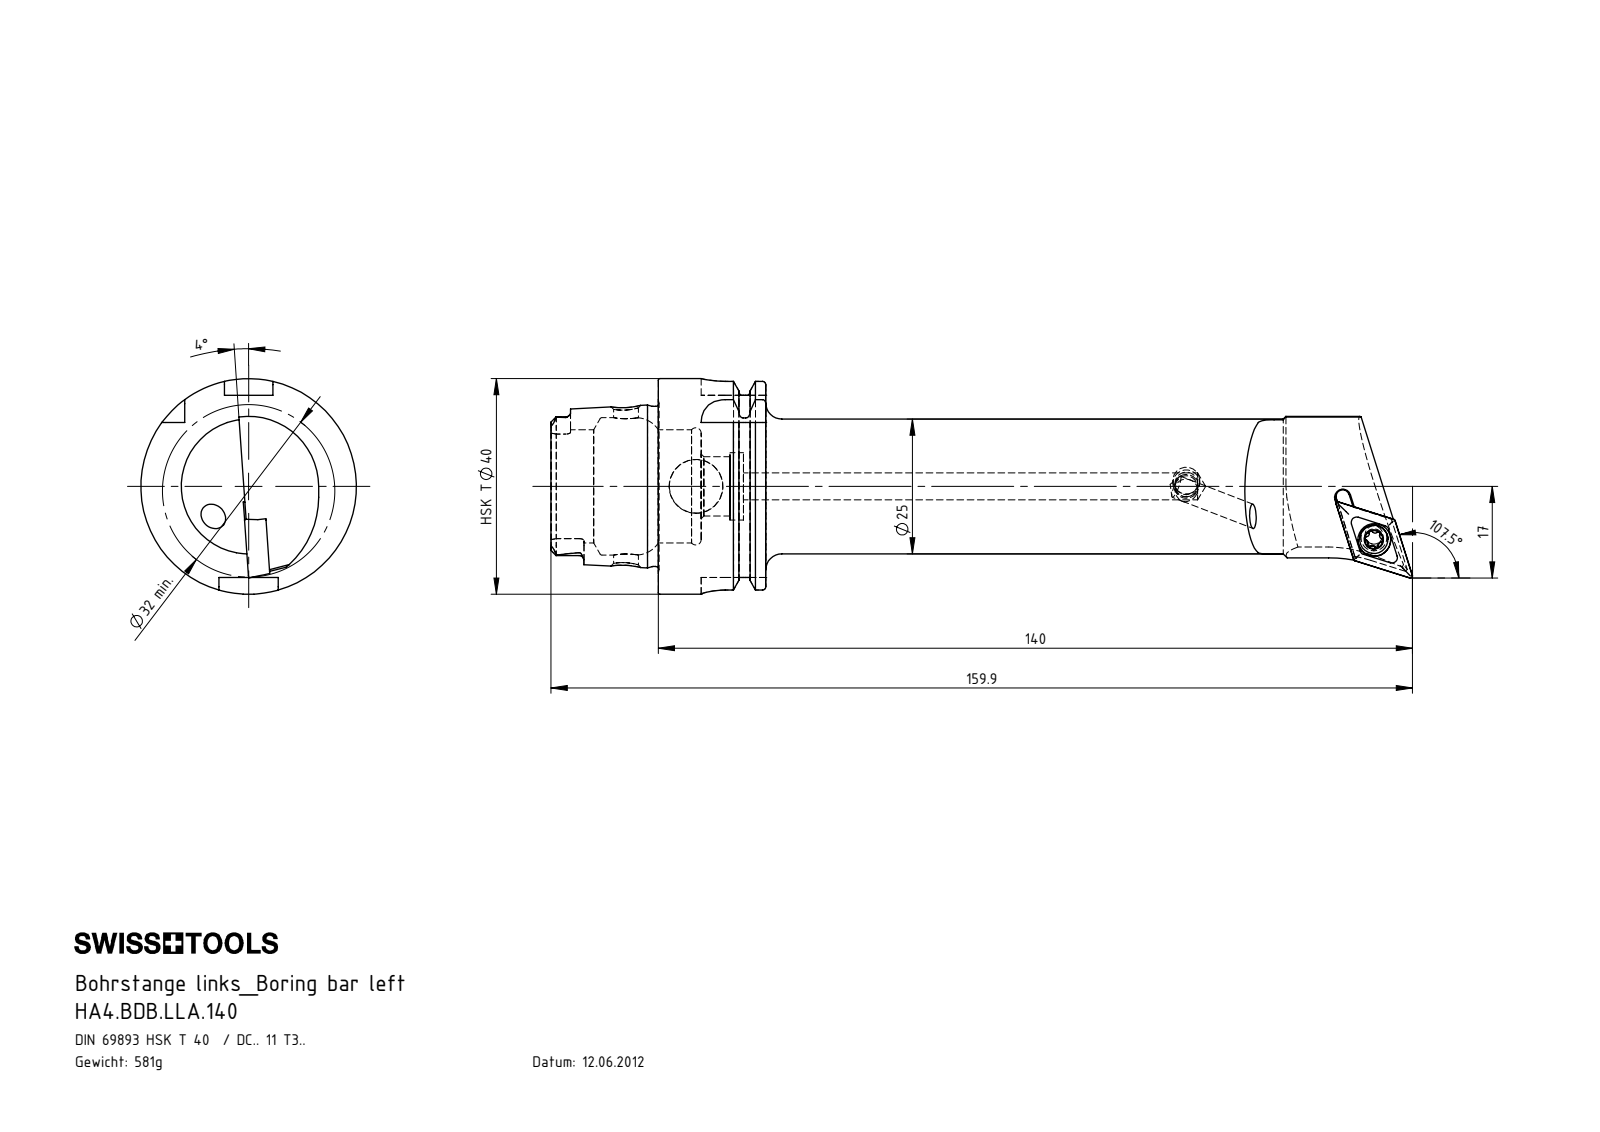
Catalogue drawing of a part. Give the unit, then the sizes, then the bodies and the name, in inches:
Units: inches
Overall size (bounding box): 6.295 × 1.575 × 1.575
Round holes (diameter × count): ⌀0.165 ×2, ⌀0.13 ×1, ⌀0.157 ×1, ⌀0.173 ×1, ⌀0.181 ×1, ⌀0.197 ×1, ⌀0.24 ×1, ⌀0.394 ×1, ⌀0.433 ×1, ⌀0.492 ×1, ⌀0.827 ×1, ⌀1.004 ×1
Round bosses / shafts (diameter × count): ⌀1.575 ×1, ⌀1.368 ×1, ⌀1.17 ×1, ⌀0.984 ×1, ⌀0.207 ×1, ⌀0.197 ×1, ⌀0.157 ×1
Partial cylindrical surfaces — rounded edges, fillets, slot ends (radius × count): R0.013 ×6, R0.023 ×6, R0.035 ×6, R0.177 ×4, R0.072 ×2, R0.074 ×2, R0.049 ×1, R0.118 ×1
Main face-to-face distances: 0.785, 0.313, 0.472, 0.144, 0.783, 1.096, 1.569, 1.406, 0.622, 0.309
Volume: 4.502 in³ · Surface area: 32.22 in²
Bodies: 5 solids, 309 faces (77 planar, 92 cylindrical, 140 other)
Part name (STEP PRODUCT): KVT_MB_600_050; WCB-ER2.001.009_A; DCMT11T304; HA4-BDB.LLA.140_A (+1 more)
STEP written by: SolidWorks 2017 (AUTOMOTIVE_DESIGN)
